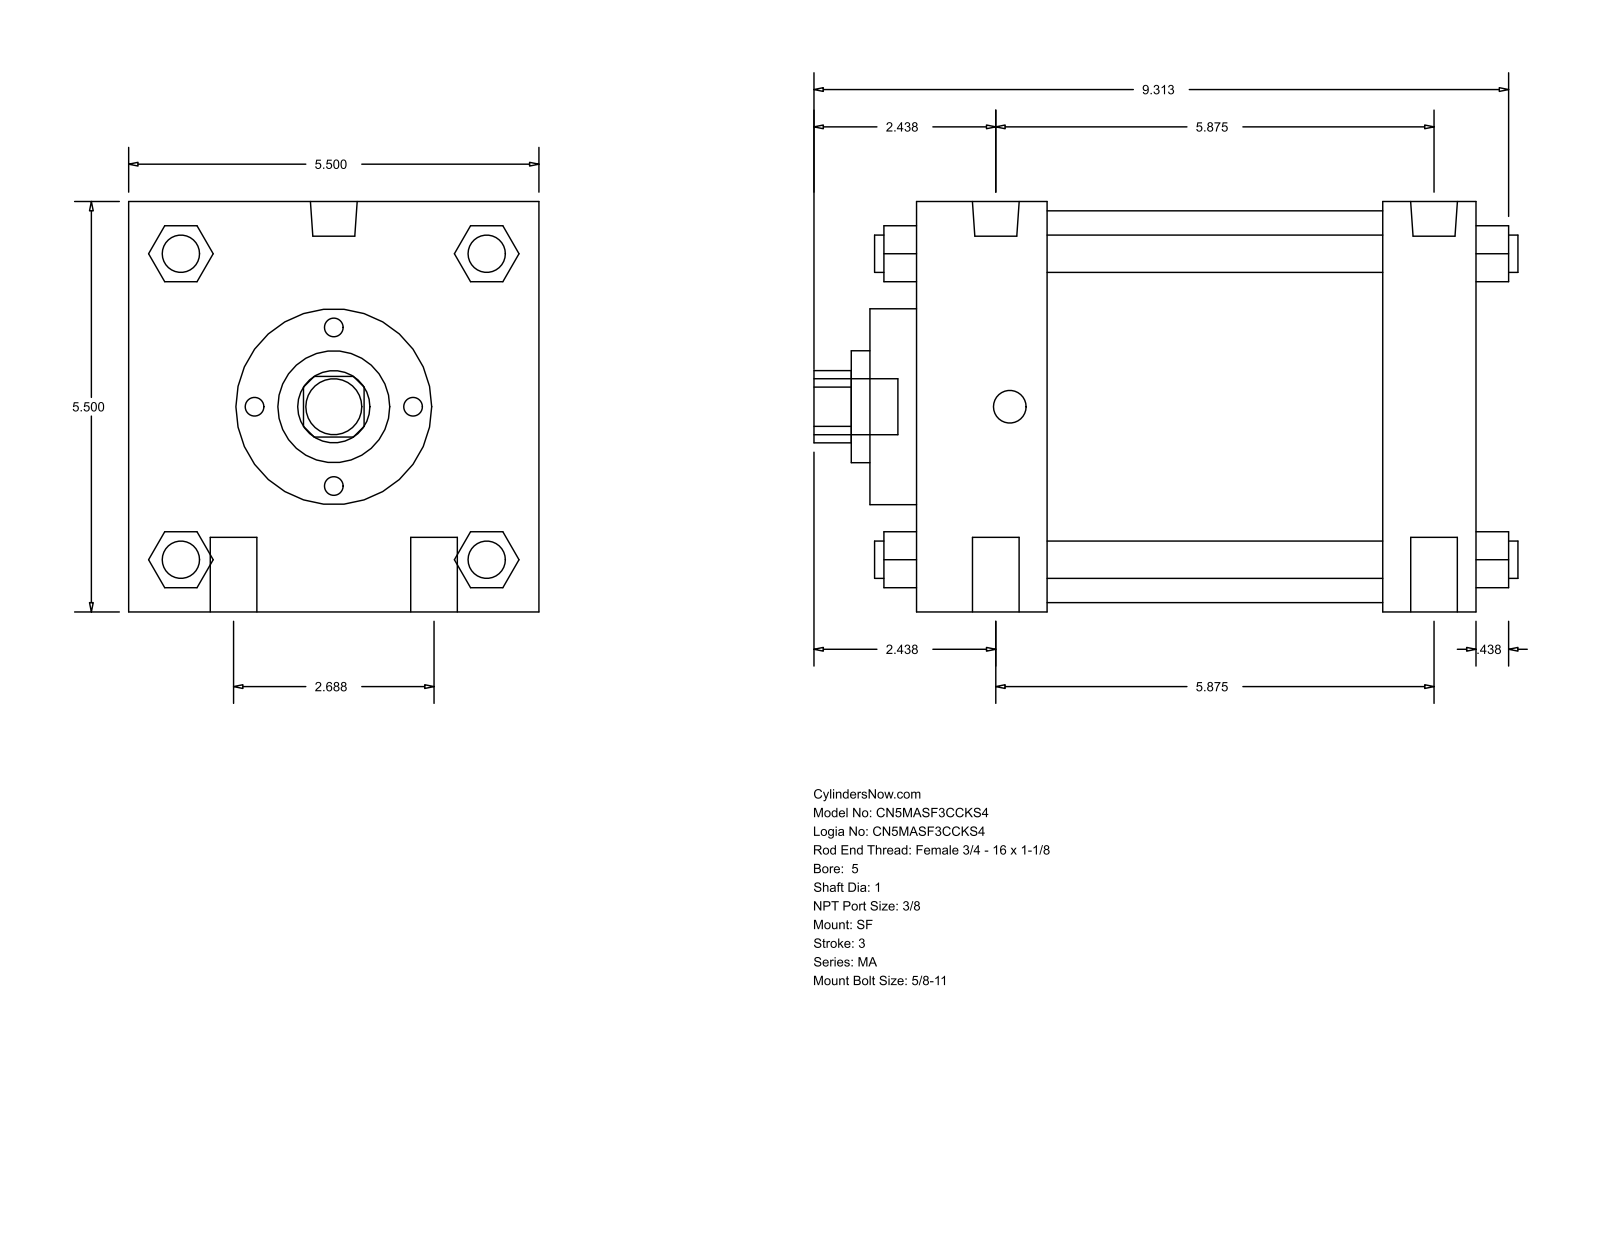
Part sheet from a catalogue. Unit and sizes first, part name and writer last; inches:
Units: inches
Overall size (bounding box): 9.437 × 5.5 × 5.5
Round holes (diameter × count): ⌀1 ×1, ⌀1.5 ×1, ⌀2.625 ×1, ⌀5.25 ×1
Round bosses / shafts (diameter × count): ⌀0.625 ×4, ⌀0.5 ×4, ⌀0.627 ×2, ⌀0.437 ×2, ⌀0.75 ×1
Partial cylindrical surfaces — rounded edges, fillets, slot ends (radius × count): R0.484 ×1
Main face-to-face distances: 5.5, 7.5, 1.75, 6.25, 4.5, 5.75, 1.25, 0.625, 2.375, 6.875
Bodies: 0 solids, 126 faces (95 planar, 31 cylindrical, 0 other)
Part name (STEP PRODUCT): MA_SF__0500_1
STEP written by: GSSL Pune (CONFIG_CONTROL_DESIGN)
